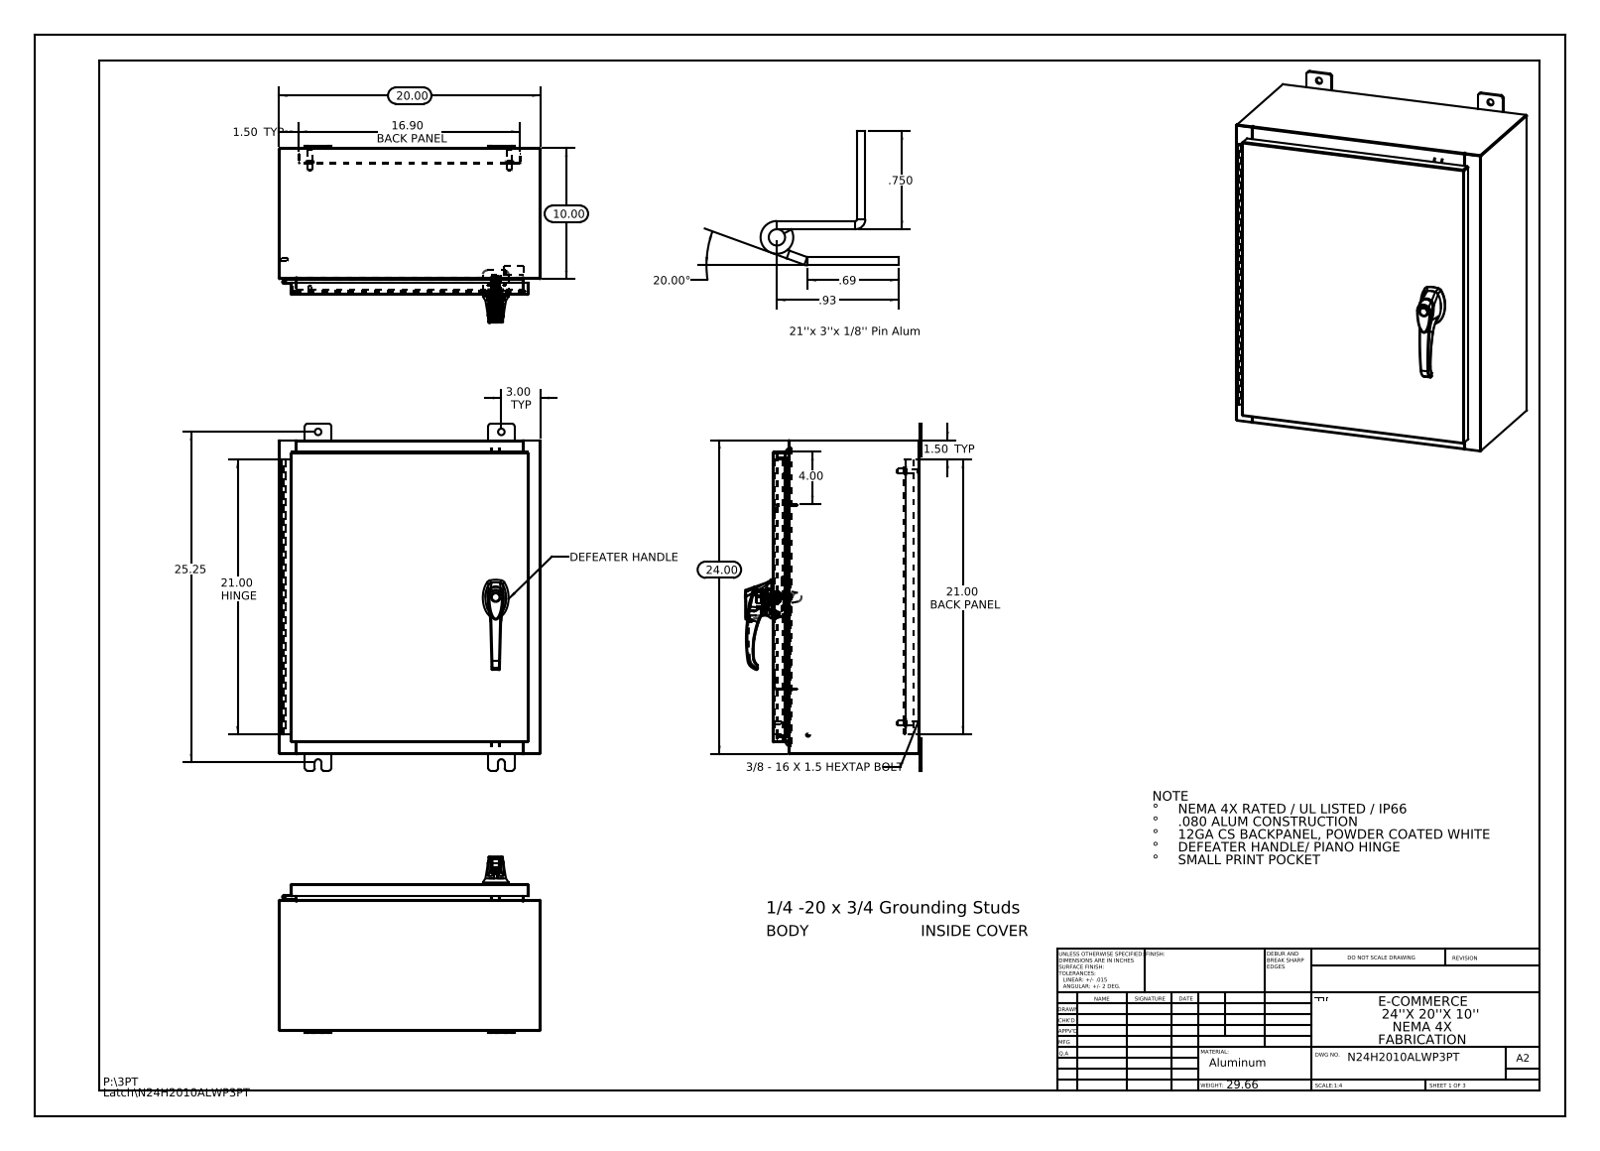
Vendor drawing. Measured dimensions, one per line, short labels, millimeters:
name: N24H2010ALWP3PT Bottom; 00005090; N24H2010ALWP3PT 263033_Industrilas; g26103103_26163303 (+8 more)
written by: SolidWorks 2013 (CONFIG_CONTROL_DESIGN)
unit: mm
bodies: 37 solids, 2498 faces (883 planar, 917 cylindrical, 698 other)
size: 673.1 × 508 × 342.8
volume: 3 397 000 mm³; area: 3 326 000 mm²
holes: 8× ⌀12.7, 4× ⌀6.4, 3× ⌀3.5, 3× ⌀4.1, 2× ⌀2, 2× ⌀5.2, 2× ⌀8, 2× ⌀11.1, 1× ⌀3.2, 1× ⌀3.2, 1× ⌀5, 1× ⌀7
bosses: 4× ⌀15.9, 4× ⌀9.5, 4× ⌀8.4, 4× ⌀4, 4× ⌀3.6, 3× ⌀8, 3× ⌀6, 1× ⌀30
rounds: 37× R3, 33× R0.2, 24× R4.8, 22× R0.3, 18× R2.2, 15× R1, 12× R0.7, 6× R0.2
face distances: 1.9, 282.6, 506.1, 280.7, 284.5, 607.7, 2.6, 25.4, 27.3, 255.3
hole spacings: 195.1, 7.5, 15.9, 21.4, 31.8, 33.4, 39.6, 47.2
